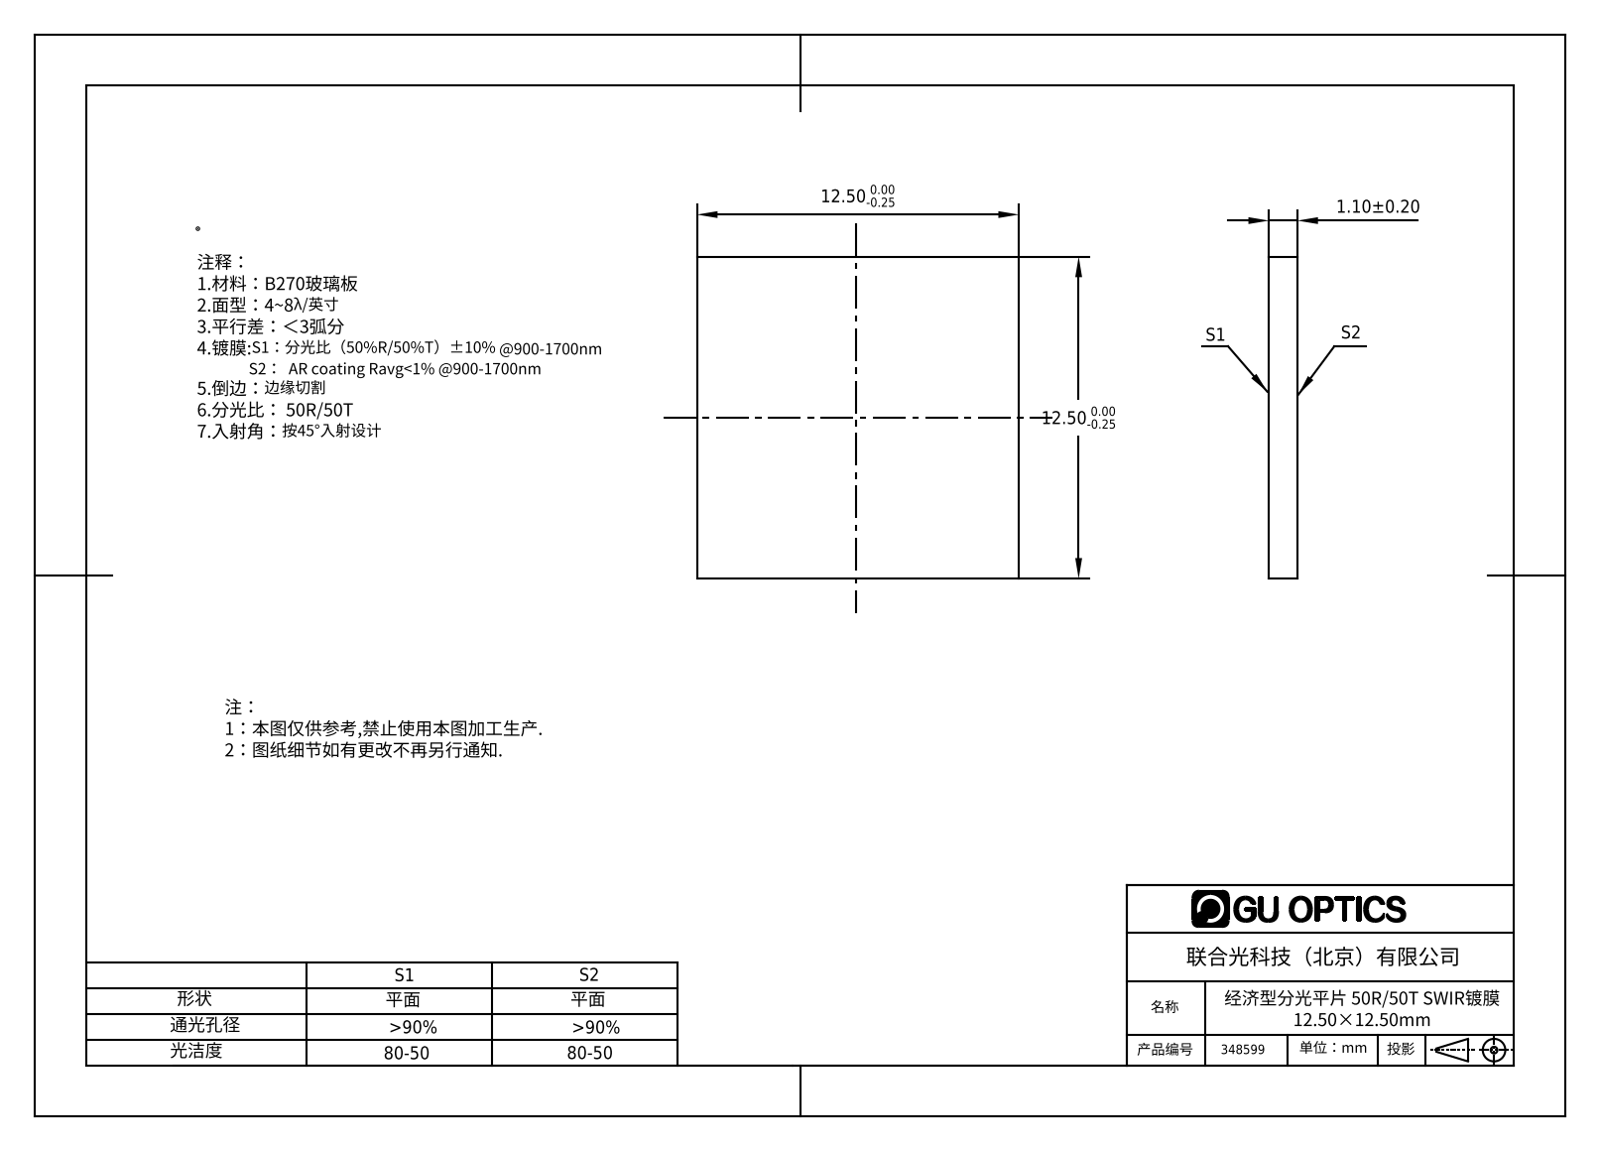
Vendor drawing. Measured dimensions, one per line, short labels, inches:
name: 348501
written by: SolidWorks 2016 (CONFIG_CONTROL_DESIGN)
unit: in
bodies: 1 solid, 6 faces (6 planar, 0 cylindrical, 0 other)
size: 0.492 × 0.492 × 0.043
volume: 0.01 in³; area: 0.57 in²
face distances: 0.043, 0.492
